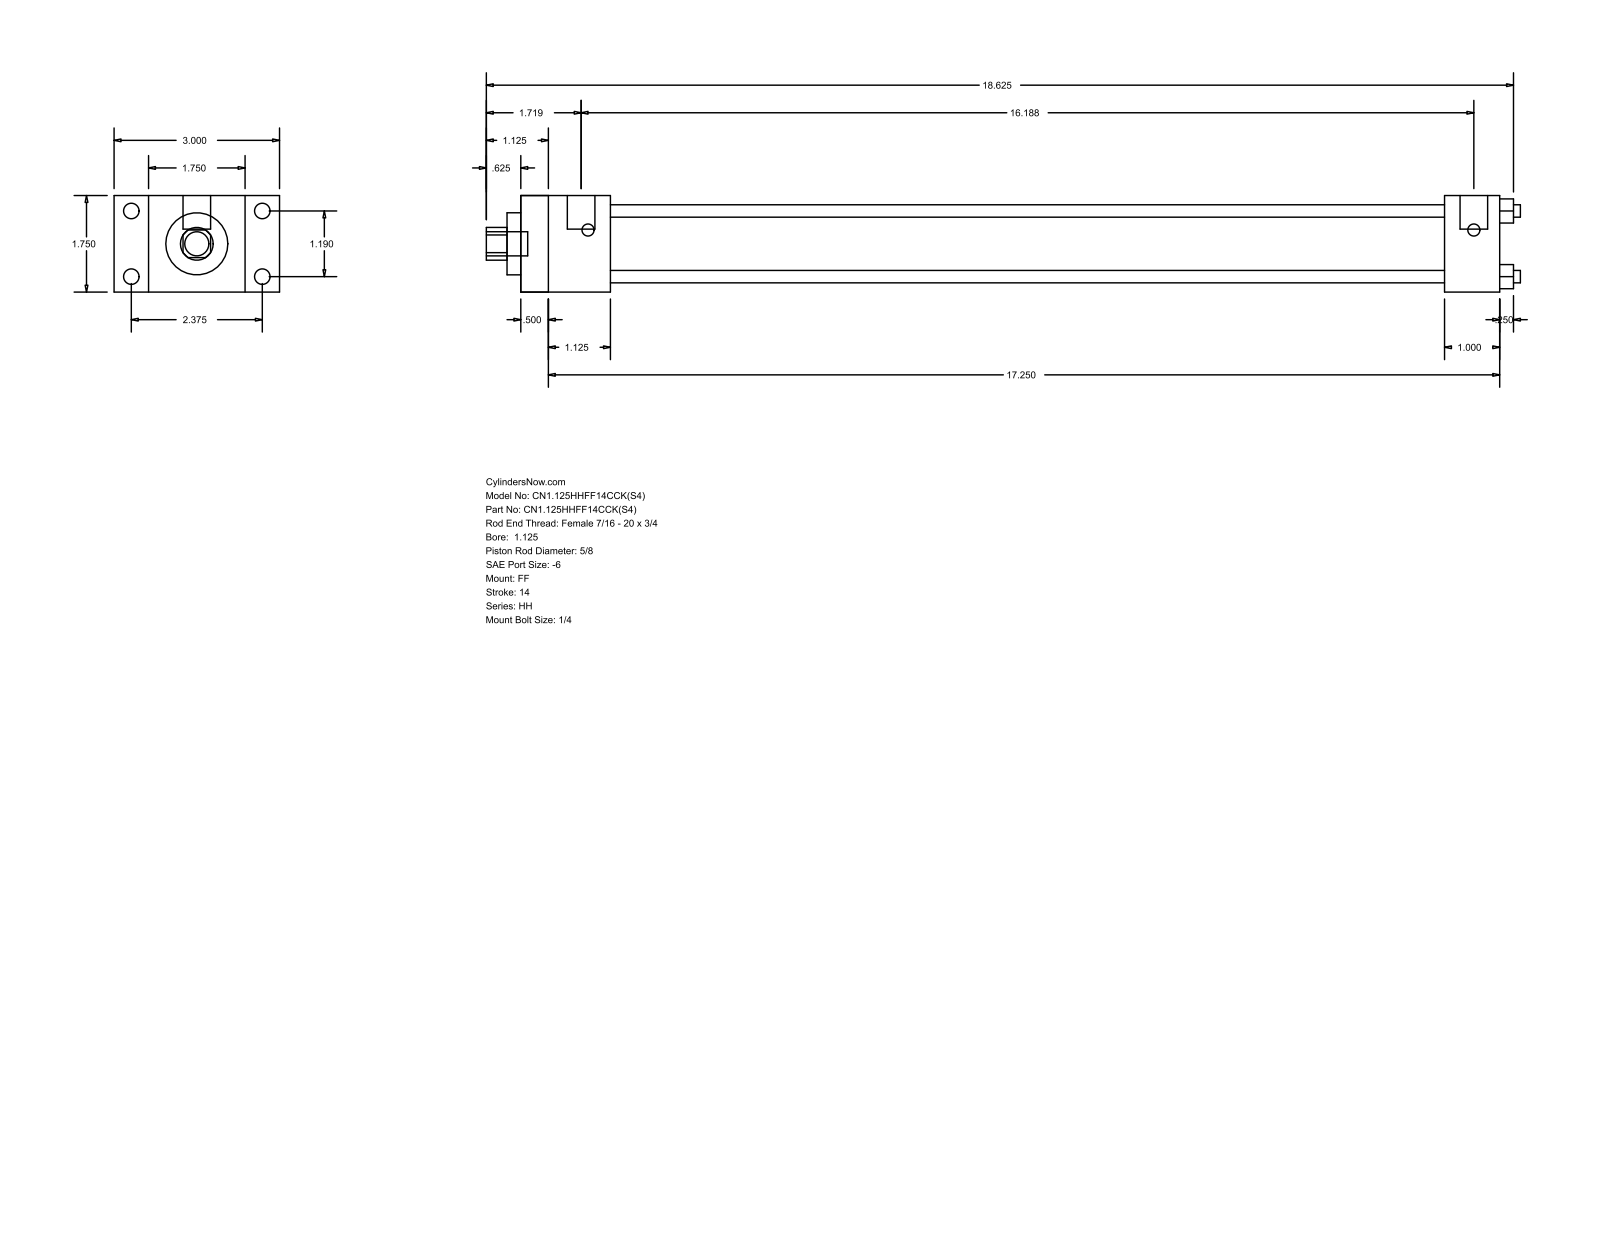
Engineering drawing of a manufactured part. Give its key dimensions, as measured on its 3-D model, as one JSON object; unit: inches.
{"part_name": "HH_FF__0112_0.625", "step_written_by": "GSSL Pune (CONFIG_CONTROL_DESIGN)", "units": "inches", "bodies": {"solids": 0, "faces": 92, "planar": 64, "cylindrical": 28, "other": 0}, "overall_size": [18.75, 3, 1.75], "round_holes": [[0.225, 4], [0.625, 1], [1.125, 1], [1.375, 1]], "round_bosses_or_shafts": [[0.281, 4], [0.219, 4], [0.5, 2], [0.437, 1]], "partial_cylinders_radius": [[0.297, 1]], "face_to_face_distances": [1.75, 17.75, 0.5, 17.25, 0.625, 2.375, 1.125, 1.625, 16.75, 16.25], "hole_center_spacings": [0.841, 1.19, 1.683]}
